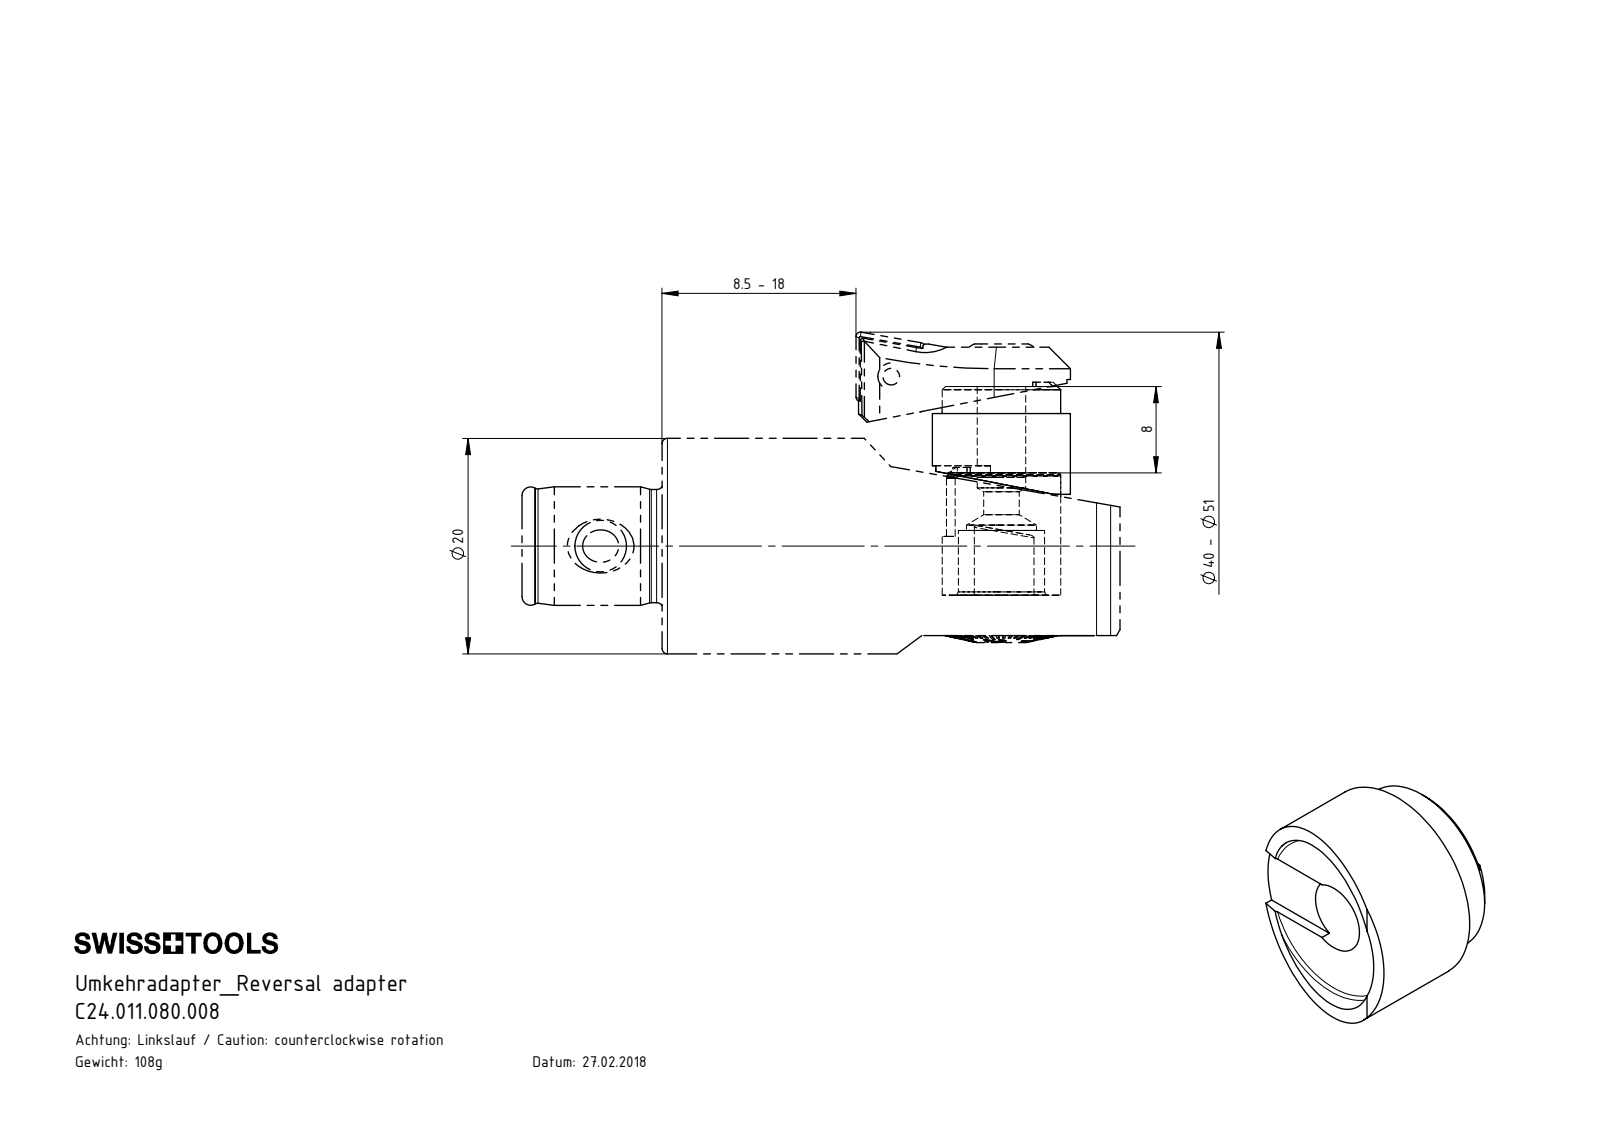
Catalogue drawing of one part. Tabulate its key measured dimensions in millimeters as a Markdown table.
| quantity | value |
| --- | --- |
| part name | C24.011.080.008; F20-U00.001.008_B |
| STEP written by | SolidWorks 2017 (CONFIG_CONTROL_DESIGN) |
| units | millimeters |
| bodies | 1 solid, 29 faces (13 planar, 11 cylindrical, 5 other) |
| overall size | 12.8 × 12.8 × 10.4 |
| volume | 843 mm³ |
| surface area | 719 mm² |
| round holes (diameter × count) | 4.5 × 1, 11 × 1 |
| round bosses / shafts (diameter × count) | 12.8 × 1 |
| partial cylindrical surfaces (radius × count) | 0.3 × 2 |
| main face-to-face distances | 8, 2.5, 5.5, 7.35, 4.85, 0.65, 0.4, 2.9, 7.75, 8.4 |
